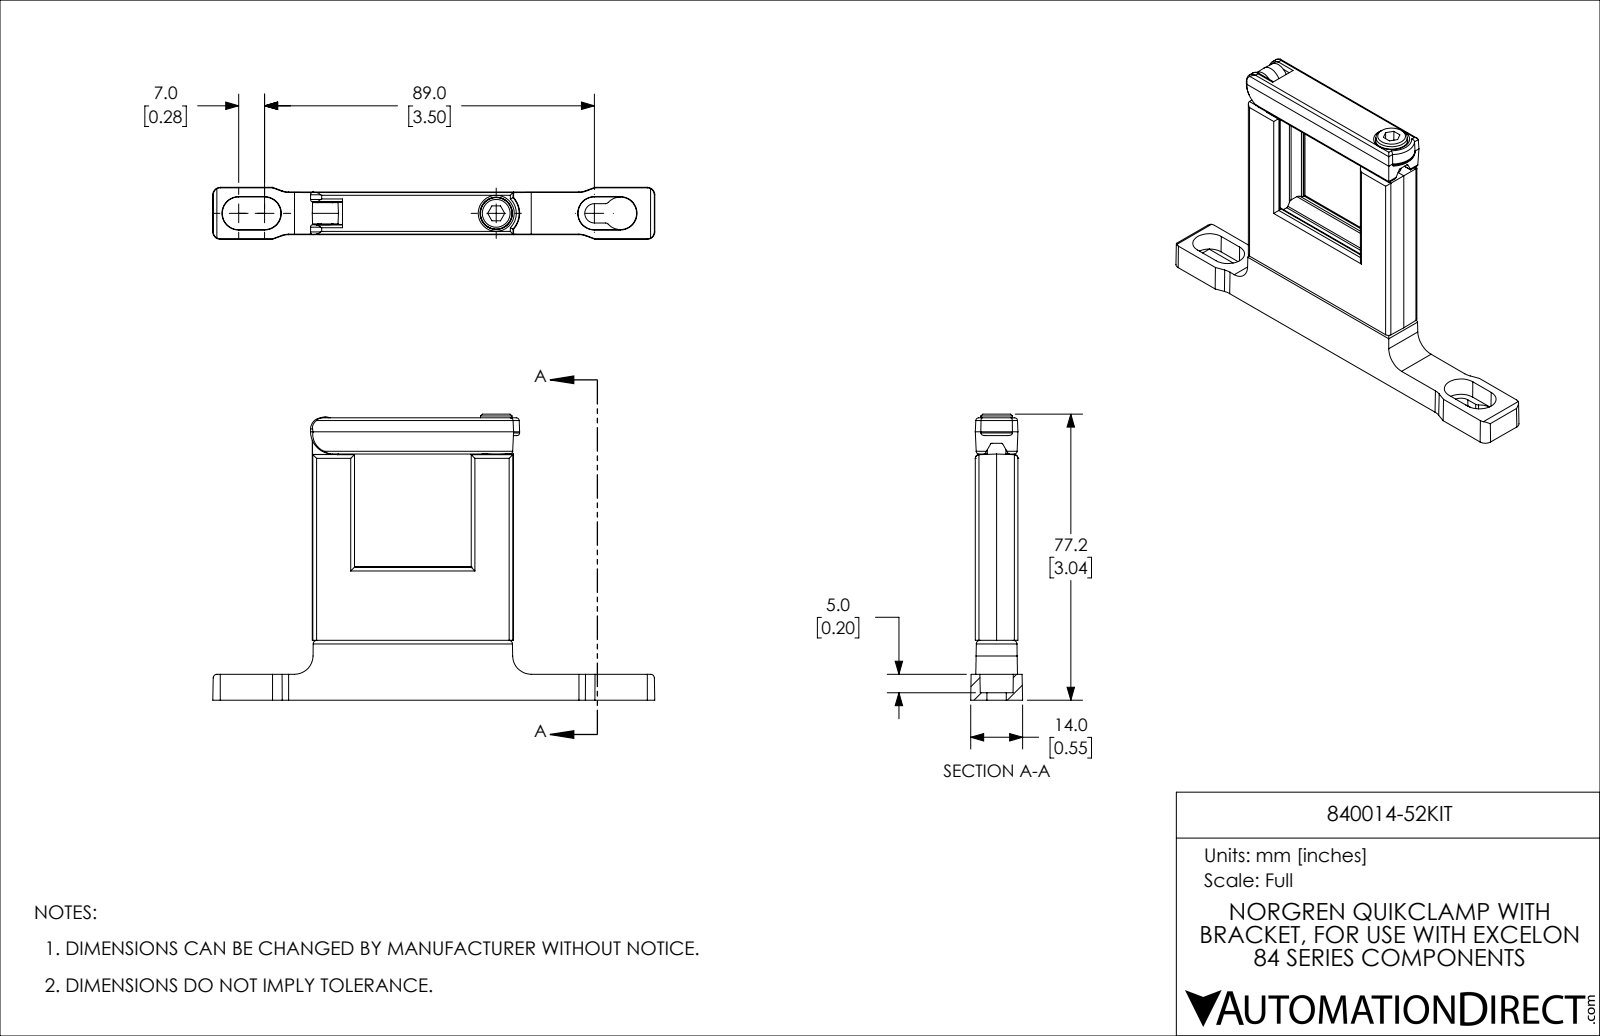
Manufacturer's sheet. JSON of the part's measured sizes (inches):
{"part_name": "840014-52KIT", "step_written_by": "SolidWorks 2021 (CONFIG_CONTROL_DESIGN)", "units": "inches", "bodies": {"solids": 1, "faces": 293, "planar": 139, "cylindrical": 109, "other": 45}, "overall_size": [4.695, 3.037, 0.551], "volume_in3": 2.119, "surface_area_in2": 26.19, "round_holes": [[0.163, 1], [0.22, 1], [0.335, 1]], "round_bosses_or_shafts": [[0.197, 2], [0.335, 1], [0.327, 1]], "partial_cylinders_radius": [[0.039, 24], [0.079, 16], [0.03, 14], [0.02, 12], [0.014, 4], [0.15, 2], [0.197, 2], [0.236, 2]], "face_to_face_distances": [0.453, 0.079, 0.374, 2.135, 0.276, 2.998, 2.722, 0.049, 2.614, 2.339], "hole_center_spacings": [0.886]}
